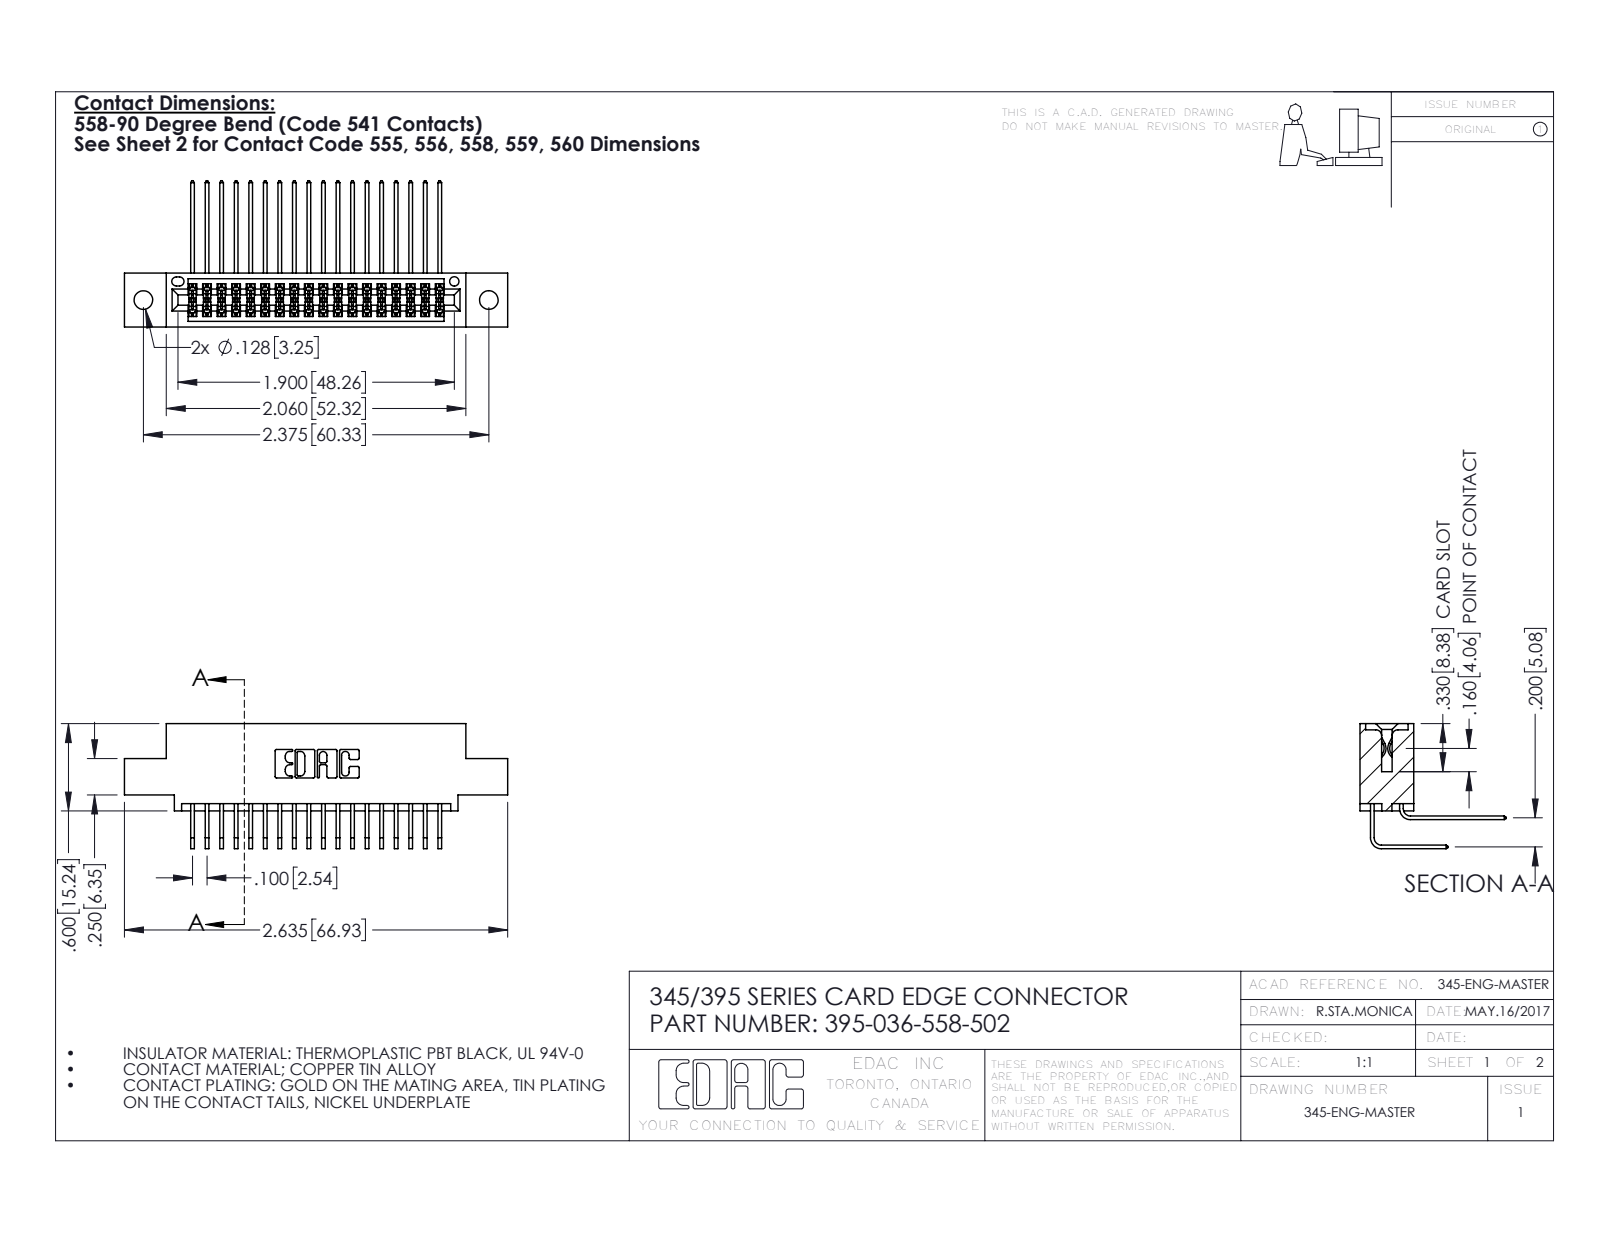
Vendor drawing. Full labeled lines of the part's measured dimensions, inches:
Part name (STEP PRODUCT): 345-292-001_558 559 Tail - 1; 345 Part_0.110 Offset - 0.128 Dia; 345-292-001_558 Tail - 2; 395-036-558-502
STEP written by: SolidWorks 2016 (CONFIG_CONTROL_DESIGN)
Units: inches
Bodies: 37 solids, 2002 faces (1344 planar, 658 cylindrical, 0 other)
Overall size (bounding box): 2.635 × 1.005 × 0.859
Volume: 0.389 in³ · Surface area: 15.12 in²
Round holes (diameter × count): ⌀0.128 ×2, ⌀0.064 ×1
Partial cylindrical surfaces — rounded edges, fillets, slot ends (radius × count): R0.006 ×55, R0.01 ×22, R0.007 ×6, R0.031 ×6, R0.026 ×3, R0.014 ×2, R0.019 ×2, R0.022 ×2
Main face-to-face distances: 0.2, 0.072, 0.298, 0.37, 0.098, 0.272, 0.025, 0.225, 0.1, 0.025
Hole centre spacings: 0.27, 2.141, 2.375
